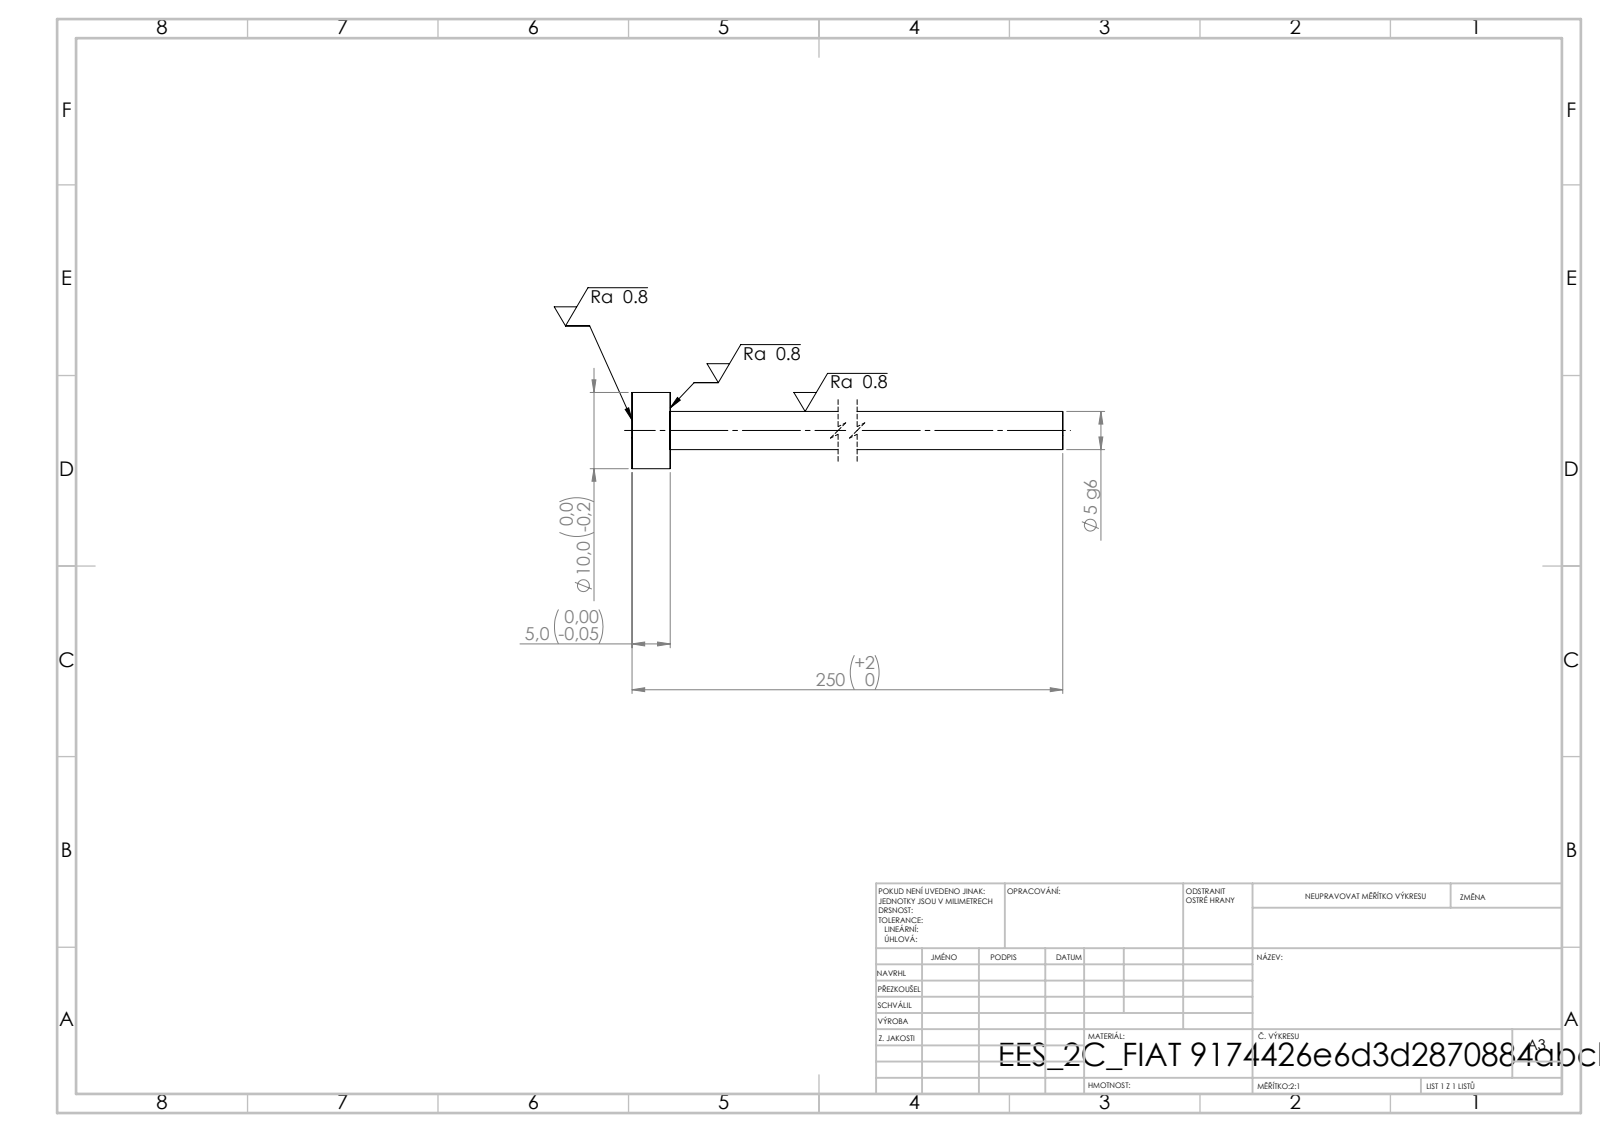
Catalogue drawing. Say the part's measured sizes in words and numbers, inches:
Its 3-D file was written by "SolidWorks 2019 (CONFIG_CONTROL_DESIGN)". It is 1 solid with 7 faces: 3 planar, 4 cylindrical and 0 other. Overall it measures 9.843 by 0.394 by 0.394 inches. Its volume is 0.318 cubic inches and its surface area 6.453 square inches. Round bosses or shafts: 1 of diameter 0.394, 1 of diameter 0.197. The main face-to-face distances are 0.197, 9.843, 9.646.
